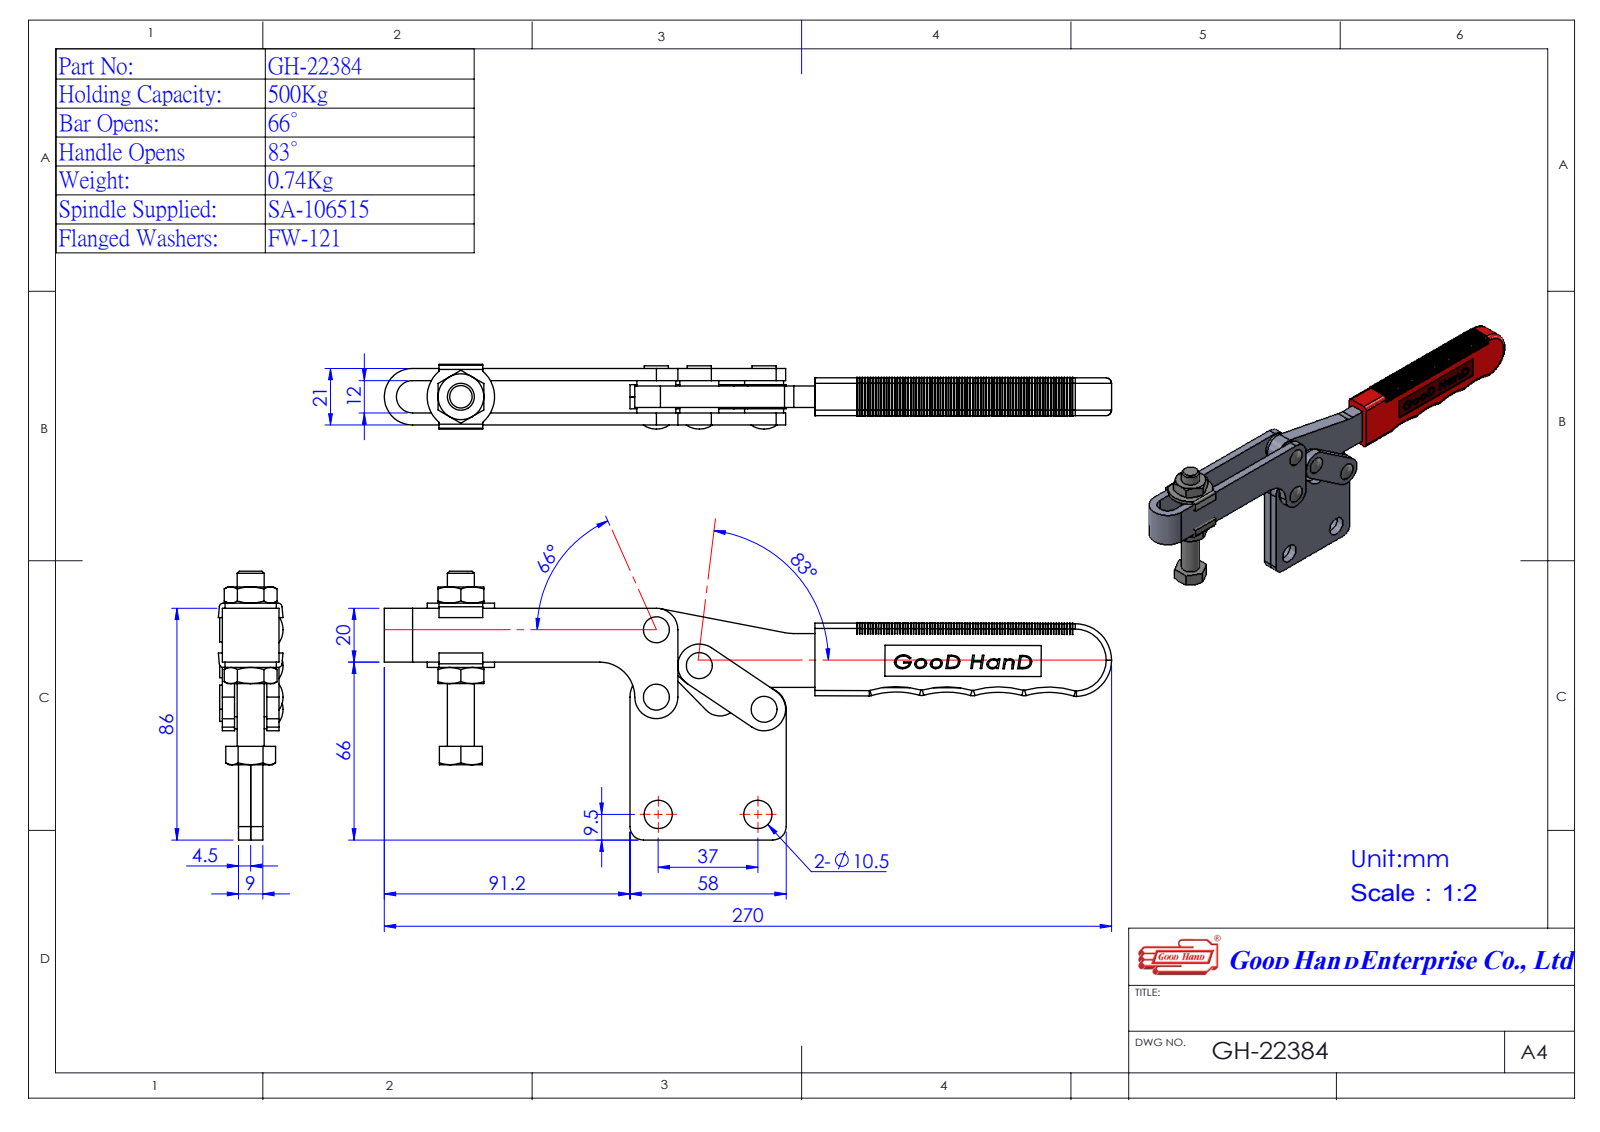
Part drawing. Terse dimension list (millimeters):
name: Group2^GH-22384(簡化)-1; Group4^GH-22384(簡化); GH-22384(簡化)-1; Group5^GH-22384(簡化)-1 (+2 more)
written by: SolidWorks 2016 (AUTOMOTIVE_DESIGN)
unit: mm
bodies: 4 solids, 274 faces (108 planar, 118 cylindrical, 48 other)
size: 270 × 99.75 × 24.02
volume: 109 631 mm³; area: 46 564 mm²
holes: 4× ⌀6, 2× ⌀10.5, 1× ⌀5.33, 1× ⌀8.5, 1× ⌀10
bosses: 4× ⌀14.5, 4× ⌀9
rounds: 5× R3, 4× R1.5, 4× R8, 4× R32, 2× R5, 1× R6, 1× R7, 1× R8
face distances: 6, 17.5, 2.5, 11.5, 3.5, 15, 16.5, 1, 4.5, 13
hole spacings: 19.78, 20.77, 25, 29, 37, 39.07, 40.25, 43.51
